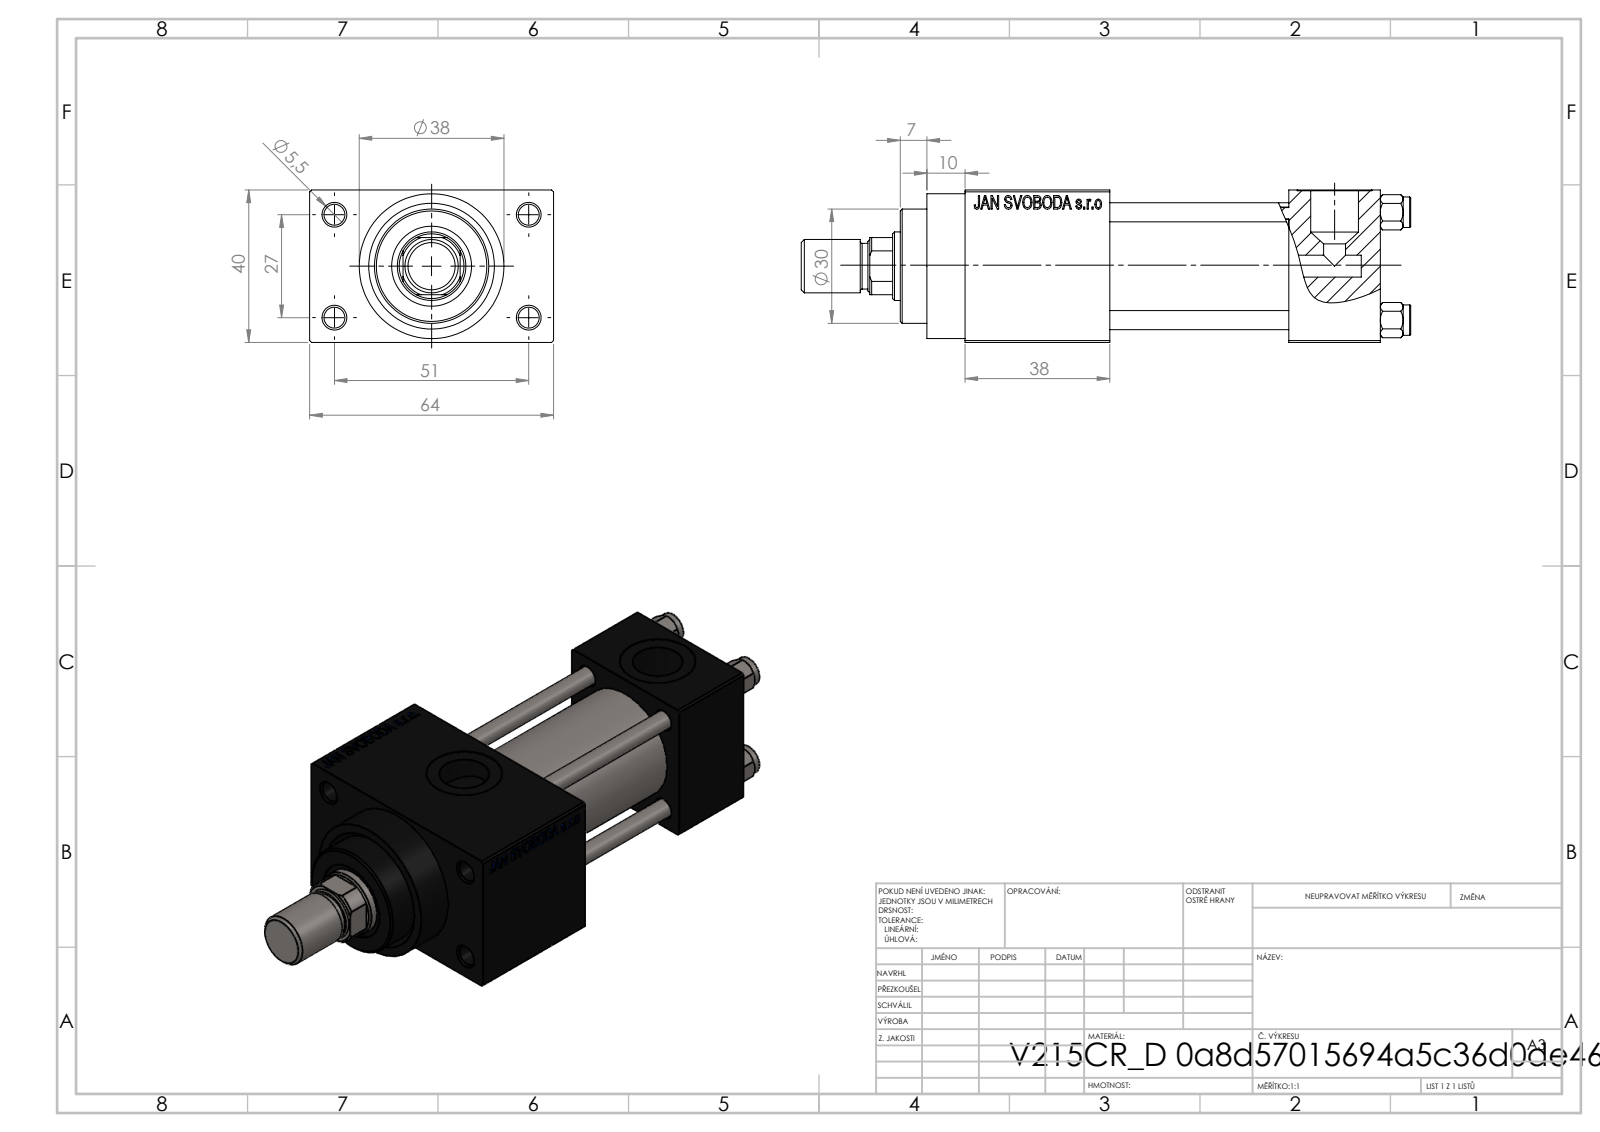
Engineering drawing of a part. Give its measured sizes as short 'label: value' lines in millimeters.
name: ROD_END_AH; V215_VC_A; NUT_M5_D; V215CR_D_TYCINKA (+2 more)
written by: SolidWorks 2019 (CONFIG_CONTROL_DESIGN)
unit: mm
bodies: 12 solids, 1116 faces (499 planar, 91 cylindrical, 526 other)
size: 160 × 64 × 40
volume: 183 346 mm³; area: 65 260 mm²
holes: 4× ⌀5, 4× ⌀5.5, 3× ⌀20, 2× ⌀7, 2× ⌀13.16, 1× ⌀8.5, 1× ⌀18, 1× ⌀21, 1× ⌀25, 1× ⌀30
bosses: 4× ⌀8, 1× ⌀38, 1× ⌀31, 1× ⌀14, 1× ⌀12
rounds: 1× R8.5
face distances: 40, 12, 52, 47, 24, 71, 64, 38, 109, 85
hole spacings: 11.37, 20.01, 28.3, 28.85, 29.89, 39.66, 48.34, 27
